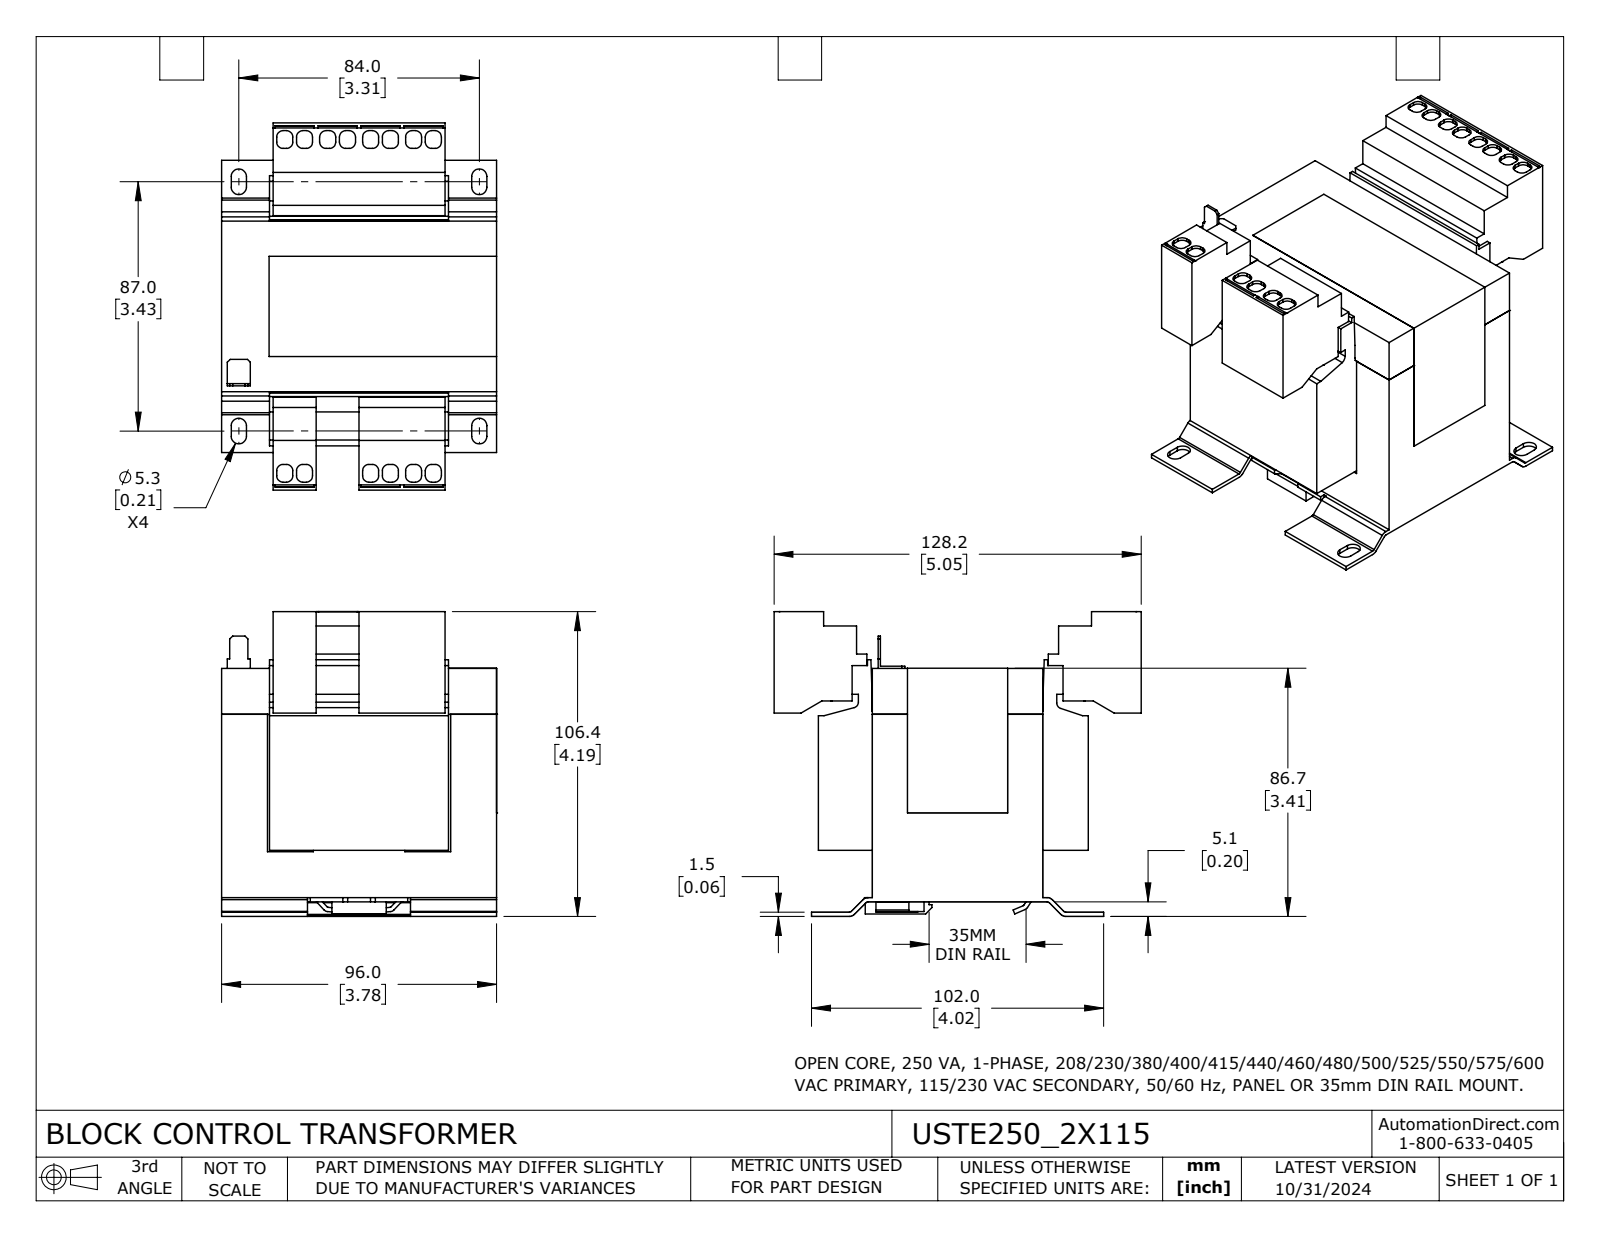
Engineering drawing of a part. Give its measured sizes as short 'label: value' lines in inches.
name: USTE250_2X115
written by: SolidWorks 2023 (CONFIG_CONTROL_DESIGN)
unit: in
bodies: 1 solid, 503 faces (409 planar, 90 cylindrical, 4 other)
size: 5.047 × 4.19 × 3.782
volume: 40.38 in³; area: 161.1 in²
rounds: 56× R0.087, 8× R0.104, 5× R0.079, 4× R0.039, 4× R0.098, 3× R0.02
face distances: 0.63, 0.659, 3.12, 0.709, 3.15, 0.03, 2.49, 2.52, 2.461, 2.343
